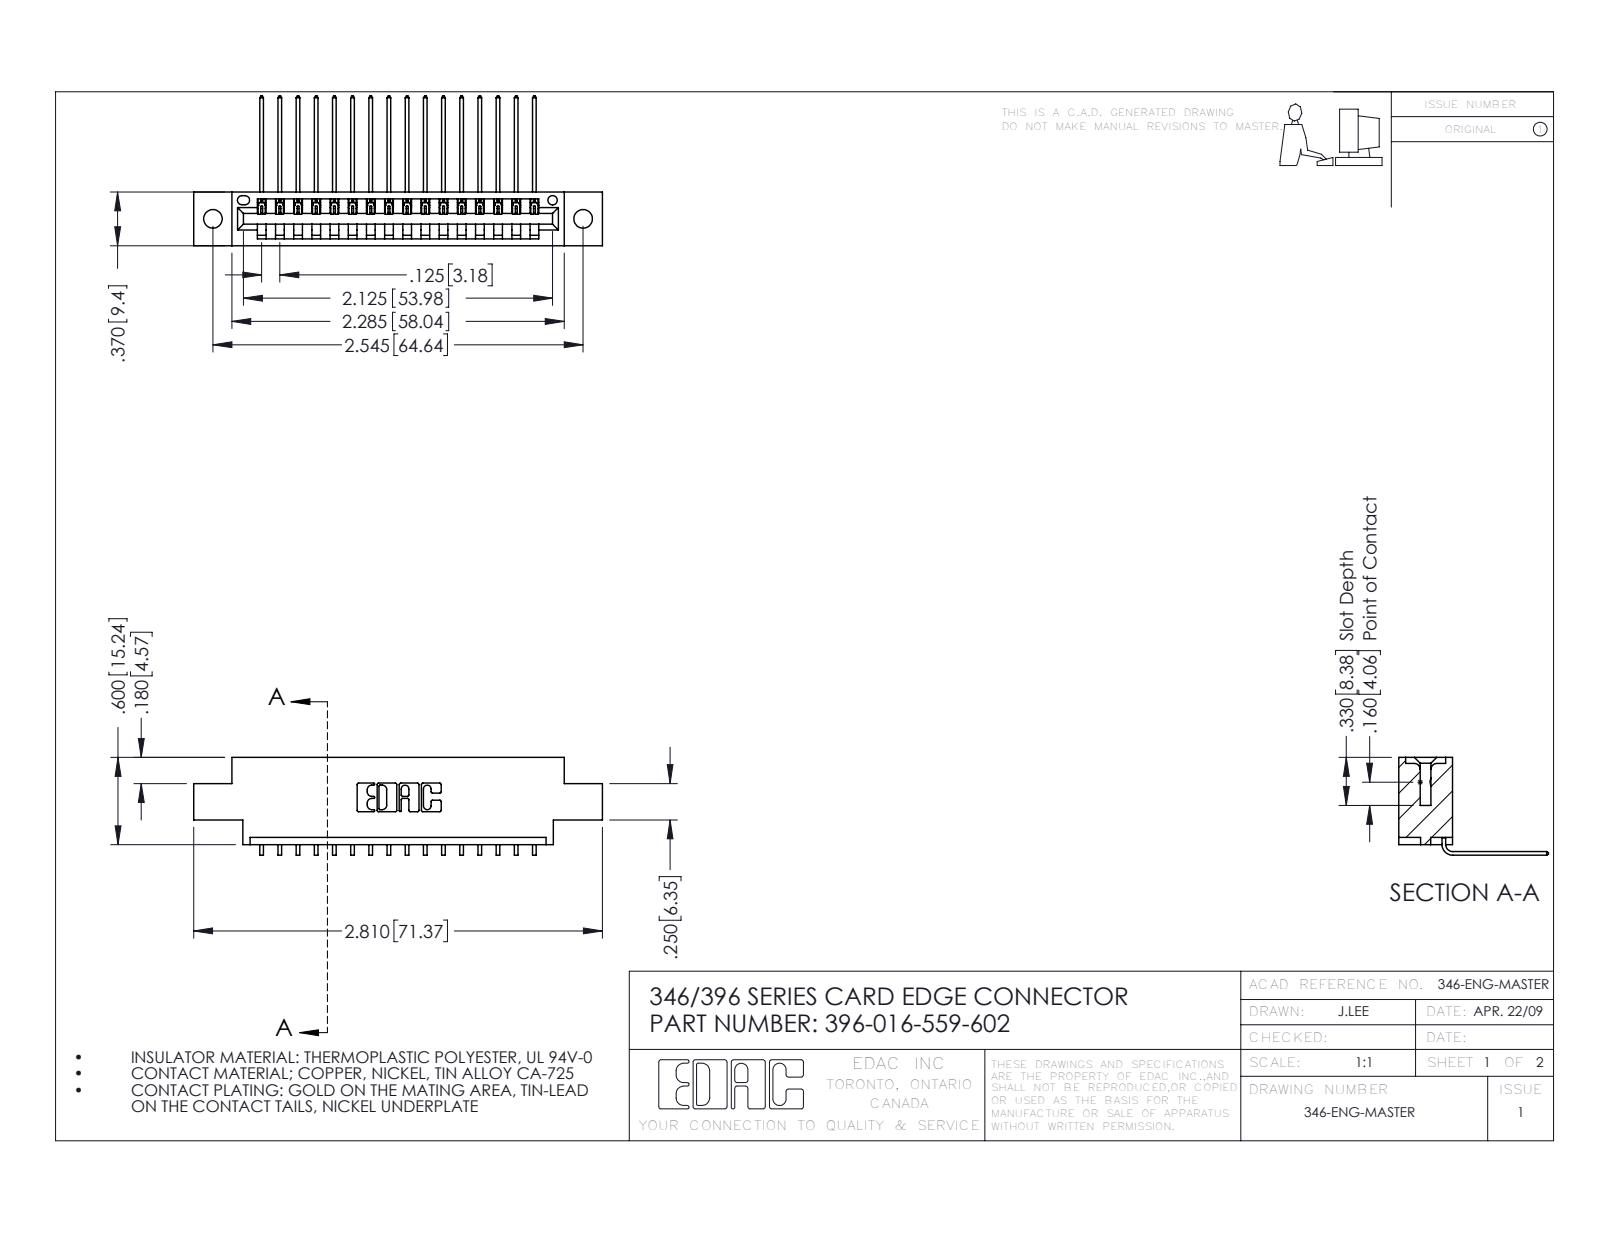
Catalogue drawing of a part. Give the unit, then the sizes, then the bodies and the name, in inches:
Units: inches
Overall size (bounding box): 2.81 × 1.03 × 0.673
Round holes (diameter × count): ⌀0.128 ×2, ⌀0.064 ×1
Partial cylindrical surfaces — rounded edges, fillets, slot ends (radius × count): R0.006 ×32, R0.01 ×22, R0.007 ×6, R0.031 ×6, R0.026 ×3, R0.031 ×2, R0.04 ×2, R0.014 ×1
Main face-to-face distances: 0.048, 0.37, 0.322, 0.25, 0.025, 0.072, 0.148, 0.222, 0.1, 0.174
Hole centre spacings: 0.246, 2.338, 2.545
Volume: 0.398 in³ · Surface area: 12.51 in²
Bodies: 17 solids, 1086 faces (752 planar, 334 cylindrical, 0 other)
Part name (STEP PRODUCT): 346 Part_0.170 Offset - 0.128 Dia; 345-292-001_558 559 Tail - 1; 396-016-559-602
STEP written by: SolidWorks 2016 (CONFIG_CONTROL_DESIGN)
